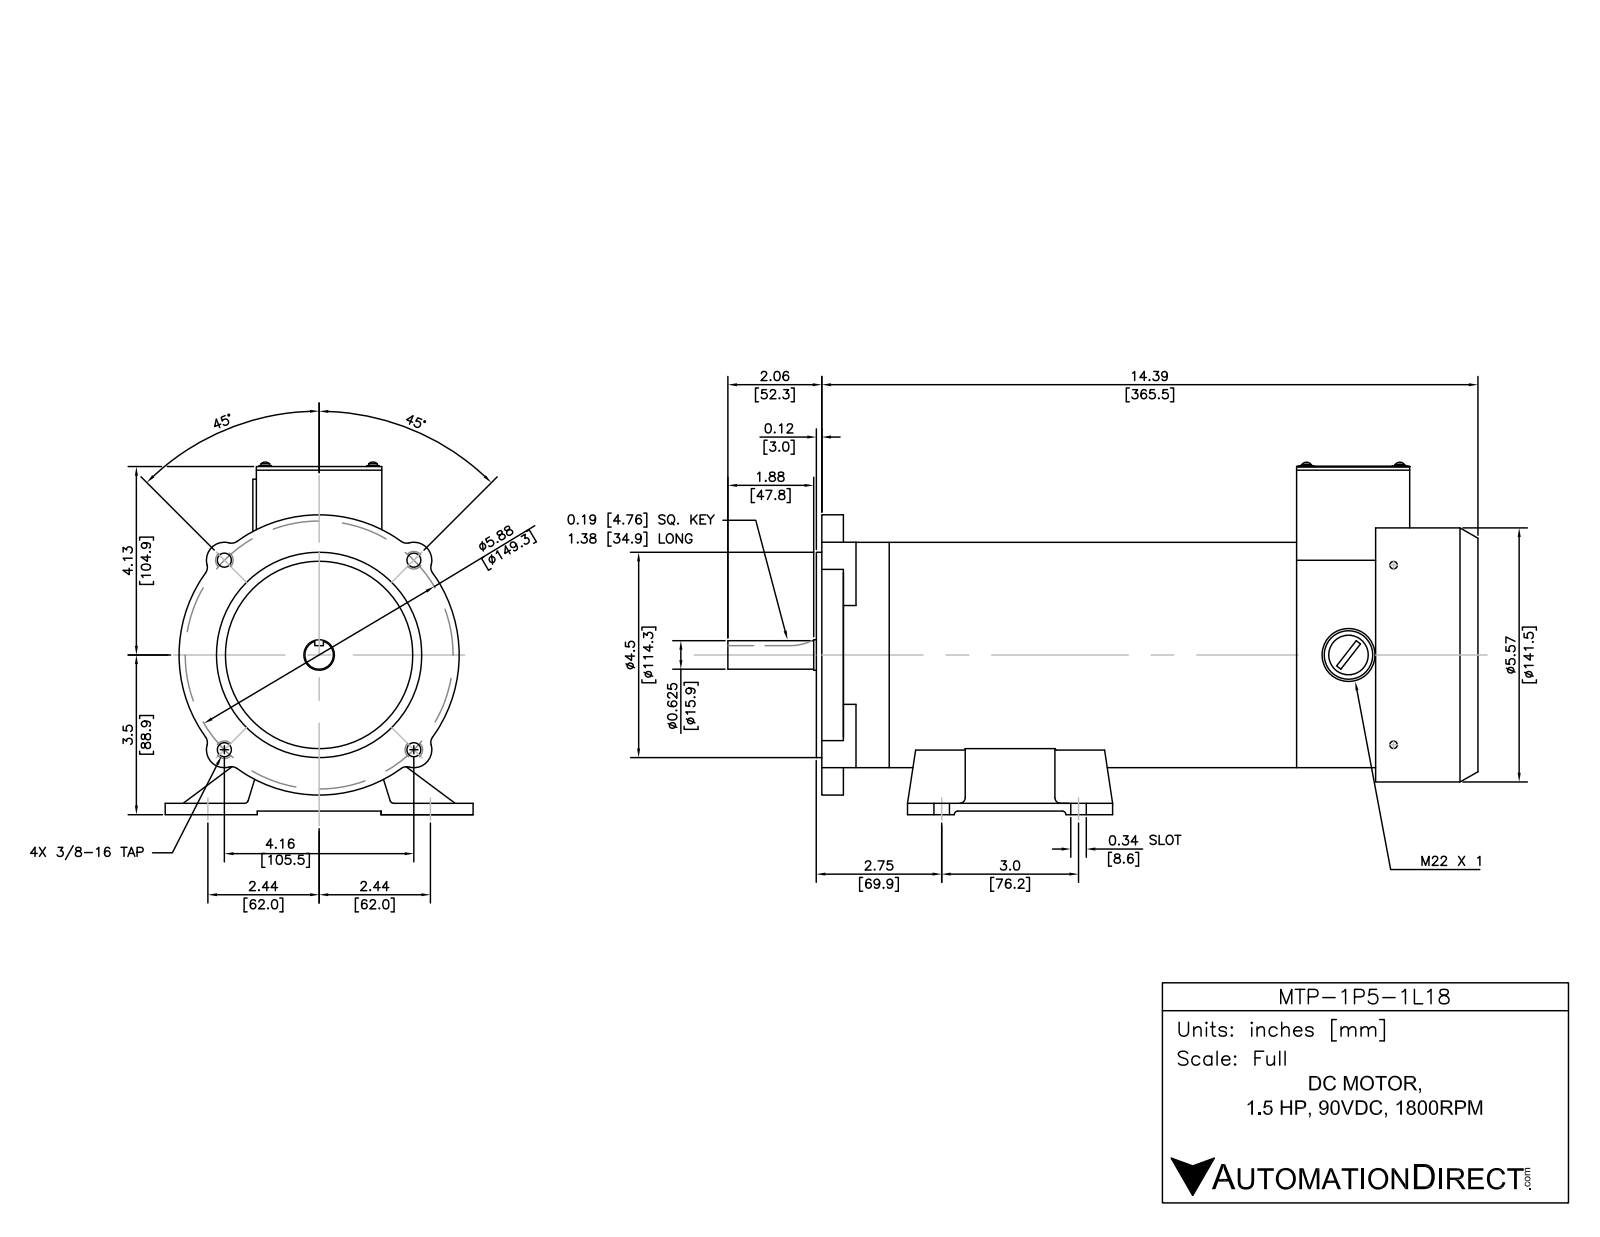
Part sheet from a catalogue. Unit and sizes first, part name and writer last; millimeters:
Units: millimetres
Overall size (bounding box): 419.2 × 191 × 165
Round holes (diameter × count): ⌀3.3 ×10, ⌀5 ×8, ⌀1.7 ×2, ⌀4.3 ×2, ⌀5.2 ×2, ⌀6 ×2, ⌀7 ×2, ⌀7.6 ×2, ⌀9.5 ×2, ⌀10 ×2, ⌀18.5 ×2, ⌀2.5 ×1
Round bosses / shafts (diameter × count): ⌀4 ×10, ⌀9 ×8, ⌀8.4 ×8, ⌀9.9 ×2, ⌀156 ×1, ⌀141.6 ×1, ⌀140 ×1, ⌀125.4 ×1
Partial cylindrical surfaces — rounded edges, fillets, slot ends (radius × count): R0.5 ×70, R5 ×38, R1 ×28, R2.5 ×18, R6 ×10, R10 ×9, R3 ×8, R4 ×8
Main face-to-face distances: 2.5, 2, 4, 1.5, 38.5, 328.4, 329.9, 0.8, 325.9, 366.9
Hole centre spacings: 30.1, 55, 57.5, 60, 69.8, 2.6, 9.1, 23.8
Volume: 1 373 000 mm³ · Surface area: 579 700 mm²
Bodies: 33 solids, 1839 faces (567 planar, 873 cylindrical, 399 other)
Part name (STEP PRODUCT): WPMDC1.5-18
STEP written by: SolidWorks 2017 (AUTOMOTIVE_DESIGN)
